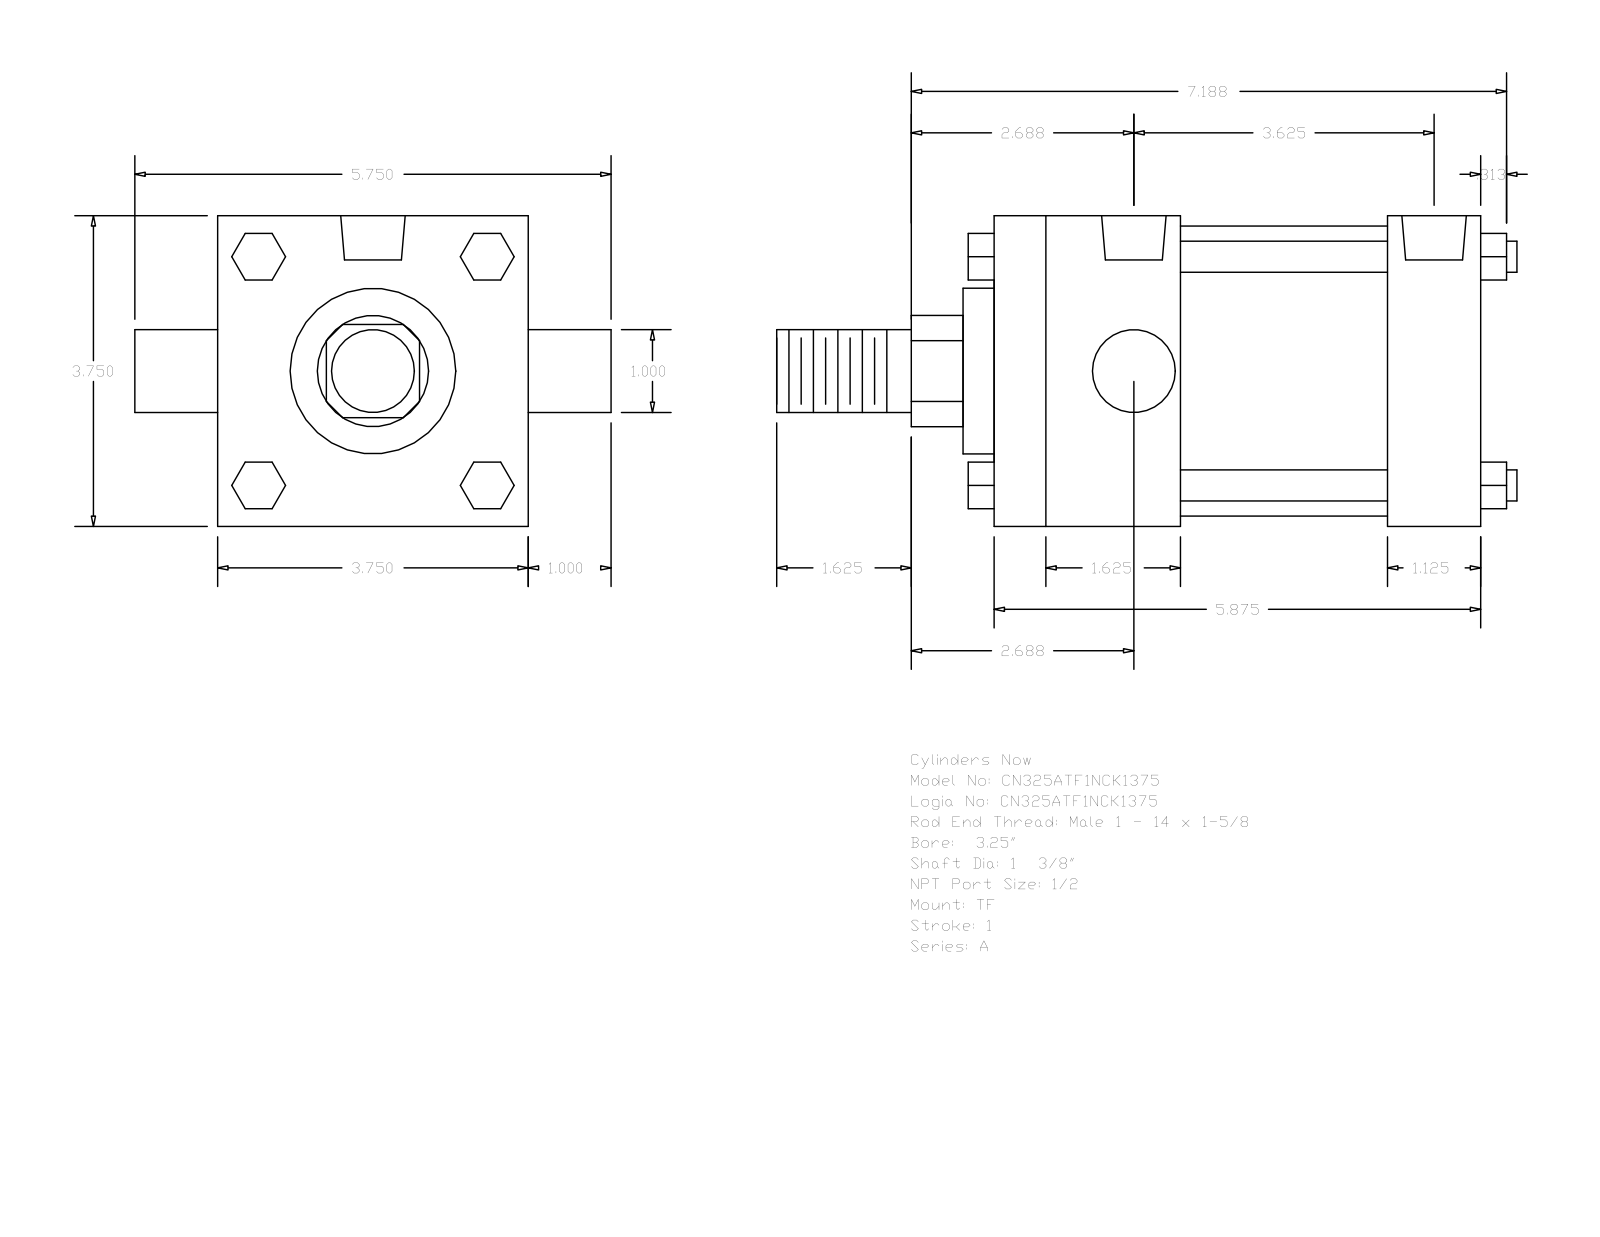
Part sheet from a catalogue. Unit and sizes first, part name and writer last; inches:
Units: inches
Overall size (bounding box): 8.937 × 5.75 × 3.75
Round holes (diameter × count): ⌀0.344 ×3, ⌀0.778 ×2
Round bosses / shafts (diameter × count): ⌀0.375 ×4, ⌀1 ×2, ⌀3.5 ×1, ⌀2 ×1, ⌀1.375 ×1
Partial cylindrical surfaces — rounded edges, fillets, slot ends (radius × count): R0.672 ×1
Main face-to-face distances: 3.75, 5.875, 4.75, 2.25, 2.5, 3.625, 1.125, 2.625, 0.375, 5.125
Hole centre spacings: 0.125, 3.5, 3.375, 3.625
Bodies: 0 solids, 120 faces (92 planar, 28 cylindrical, 0 other)
Part name (STEP PRODUCT): A_TF__0325_1.375
STEP written by: GSSL Pune (CONFIG_CONTROL_DESIGN)
